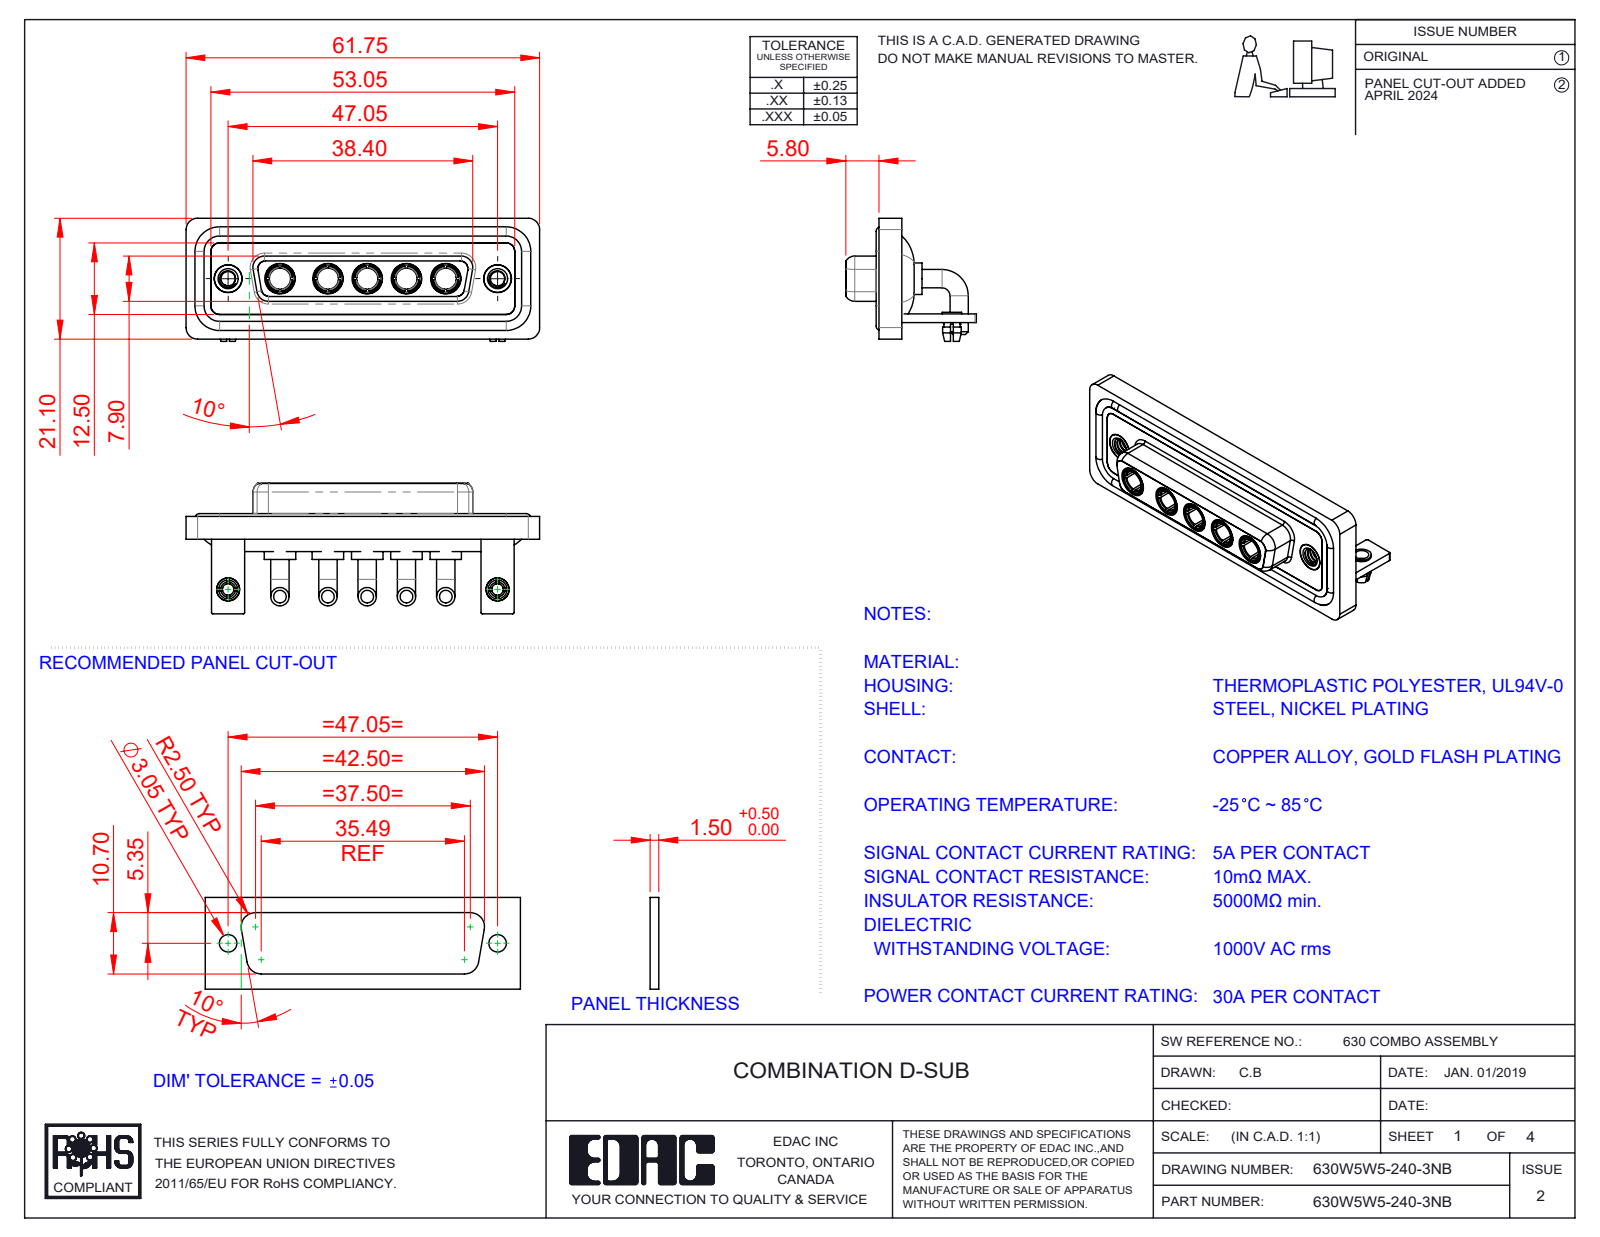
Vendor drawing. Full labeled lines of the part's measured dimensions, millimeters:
Part name (STEP PRODUCT): 630Combo Shell Front_25 Contacts; 630Combo Threaded Rivet_A; Power Socket_30A RA; 630Combo Waterproof Housing_25 Contacts (+5 more)
STEP written by: SolidWorks 2023 (CONFIG_CONTROL_DESIGN)
Units: millimetres
Bodies: 21 solids, 910 faces (318 planar, 367 cylindrical, 225 other)
Overall size (bounding box): 61.75 × 22.8 × 21.5
Volume: 8 971 mm³ · Surface area: 14 854 mm²
Round holes (diameter × count): ⌀4.85 ×7, ⌀3.7 ×5, ⌀5.3 ×5, ⌀2.5 ×4, ⌀2 ×2, ⌀3.2 ×2, ⌀4 ×2, ⌀4.05 ×2, ⌀5 ×2
Round bosses / shafts (diameter × count): ⌀3.2 ×10, ⌀5.5 ×5, ⌀5.2 ×5, ⌀4.96 ×5, ⌀4.75 ×5, ⌀3.75 ×5, ⌀1.6 ×4, ⌀4.95 ×2
Partial cylindrical surfaces — rounded edges, fillets, slot ends (radius × count): R2 ×19, R1.5 ×18, R0.25 ×16, R1.35 ×8, R1.6 ×8, R0.5 ×5, R2.1 ×5, R0.6 ×4
Main face-to-face distances: 0.4, 1.8, 2.9, 3.7, 1.5, 4.1, 1.1, 1.4, 1.6, 2.5
Hole centre spacings: 6.86, 9.04, 38.01, 47.05, 6.87, 8.38, 13.72, 13.73
